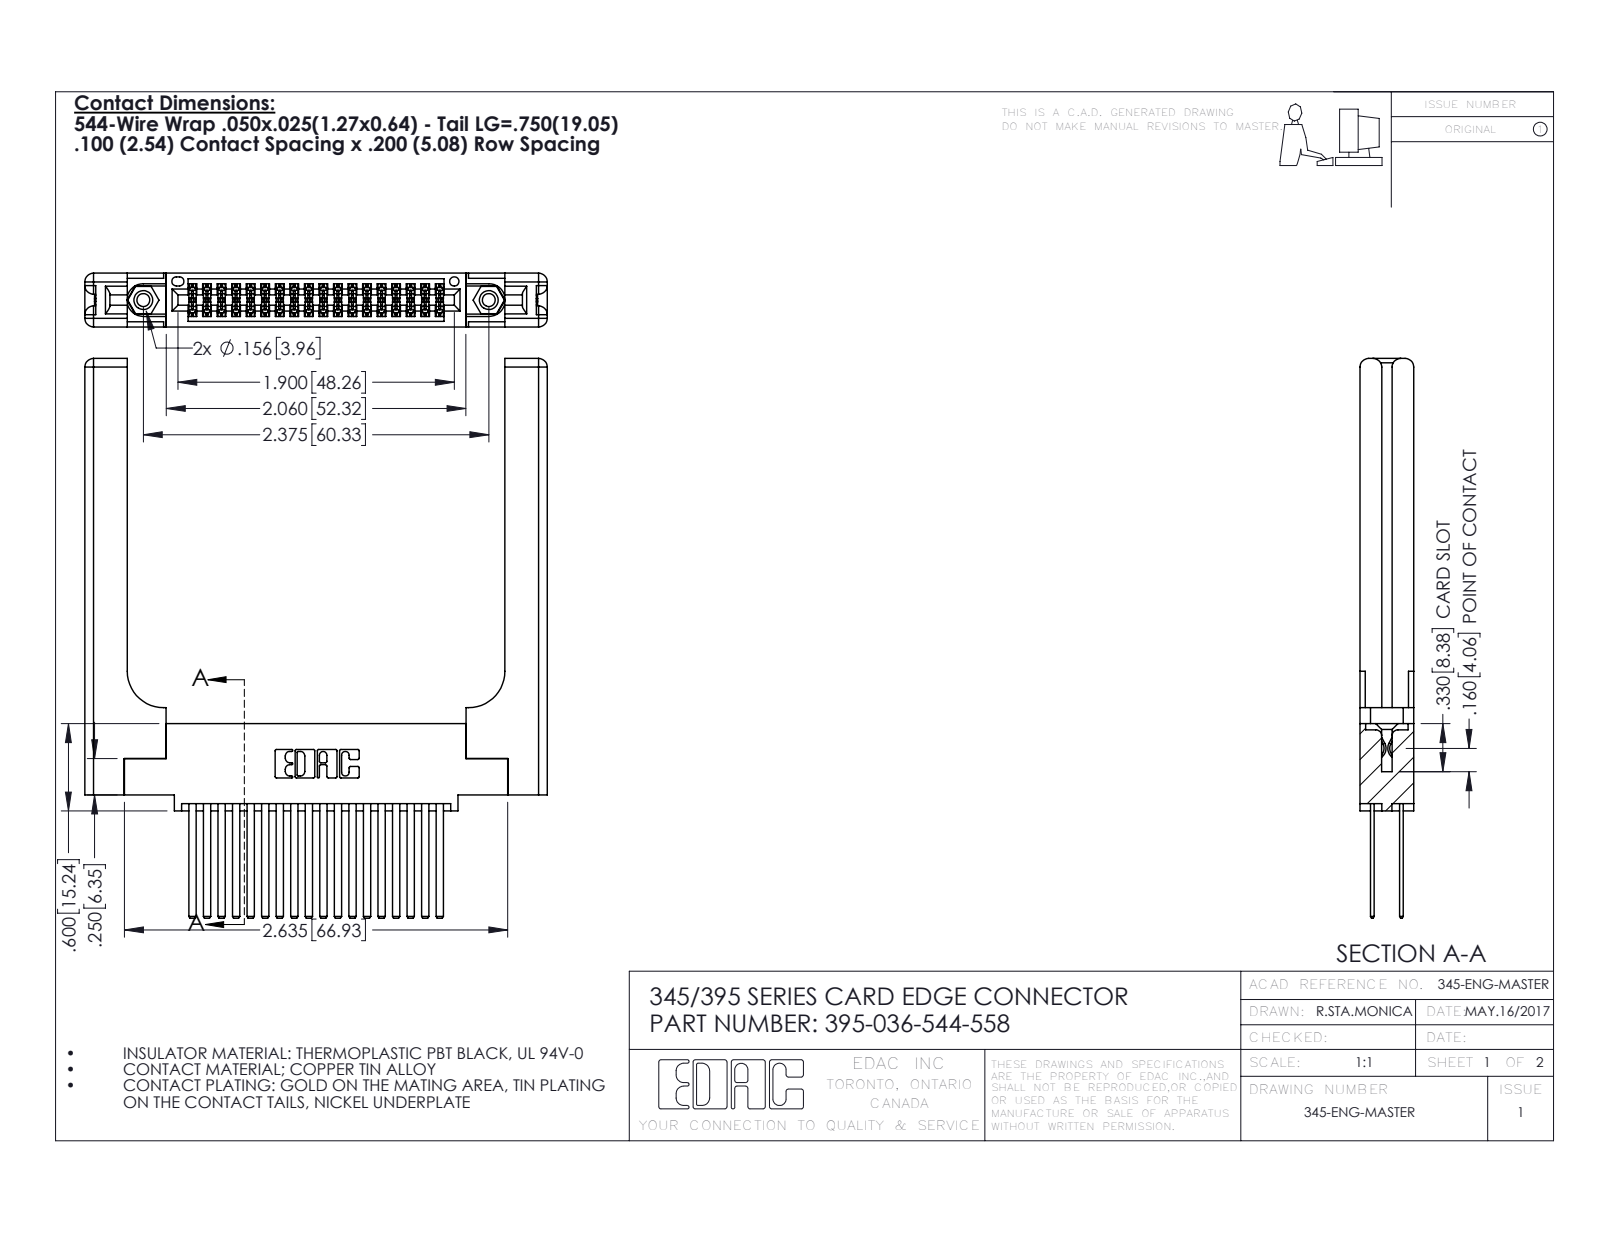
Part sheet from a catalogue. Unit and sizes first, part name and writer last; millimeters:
Units: millimetres
Overall size (bounding box): 97.7 × 80.7 × 9.4
Round holes (diameter × count): ⌀2.3 ×2, ⌀3.2 ×2, ⌀4 ×2, ⌀1.6 ×1
Round bosses / shafts (diameter × count): ⌀3.9 ×2
Partial cylindrical surfaces — rounded edges, fillets, slot ends (radius × count): R0.2 ×54, R0.3 ×22, R1.5 ×16, R0.2 ×6, R0.8 ×6, R0.7 ×3, R0.4 ×2, R0.5 ×2
Main face-to-face distances: 1.8, 7.6, 9.4, 2.5, 6.9, 0.6, 5.1, 5.7, 3.8, 3.8
Hole centre spacings: 6.9, 54.4, 60.3
Volume: 16 530 mm³ · Surface area: 18 070 mm²
Bodies: 41 solids, 1970 faces (1276 planar, 634 cylindrical, 60 other)
Part name (STEP PRODUCT): 345 Part_0.110 Offset - 0.156 Dia-TH; 345-292-001_345-293-144; 345-220-058_345-220-058; 395-036-544-558 (+1 more)
STEP written by: SolidWorks 2016 (CONFIG_CONTROL_DESIGN)
